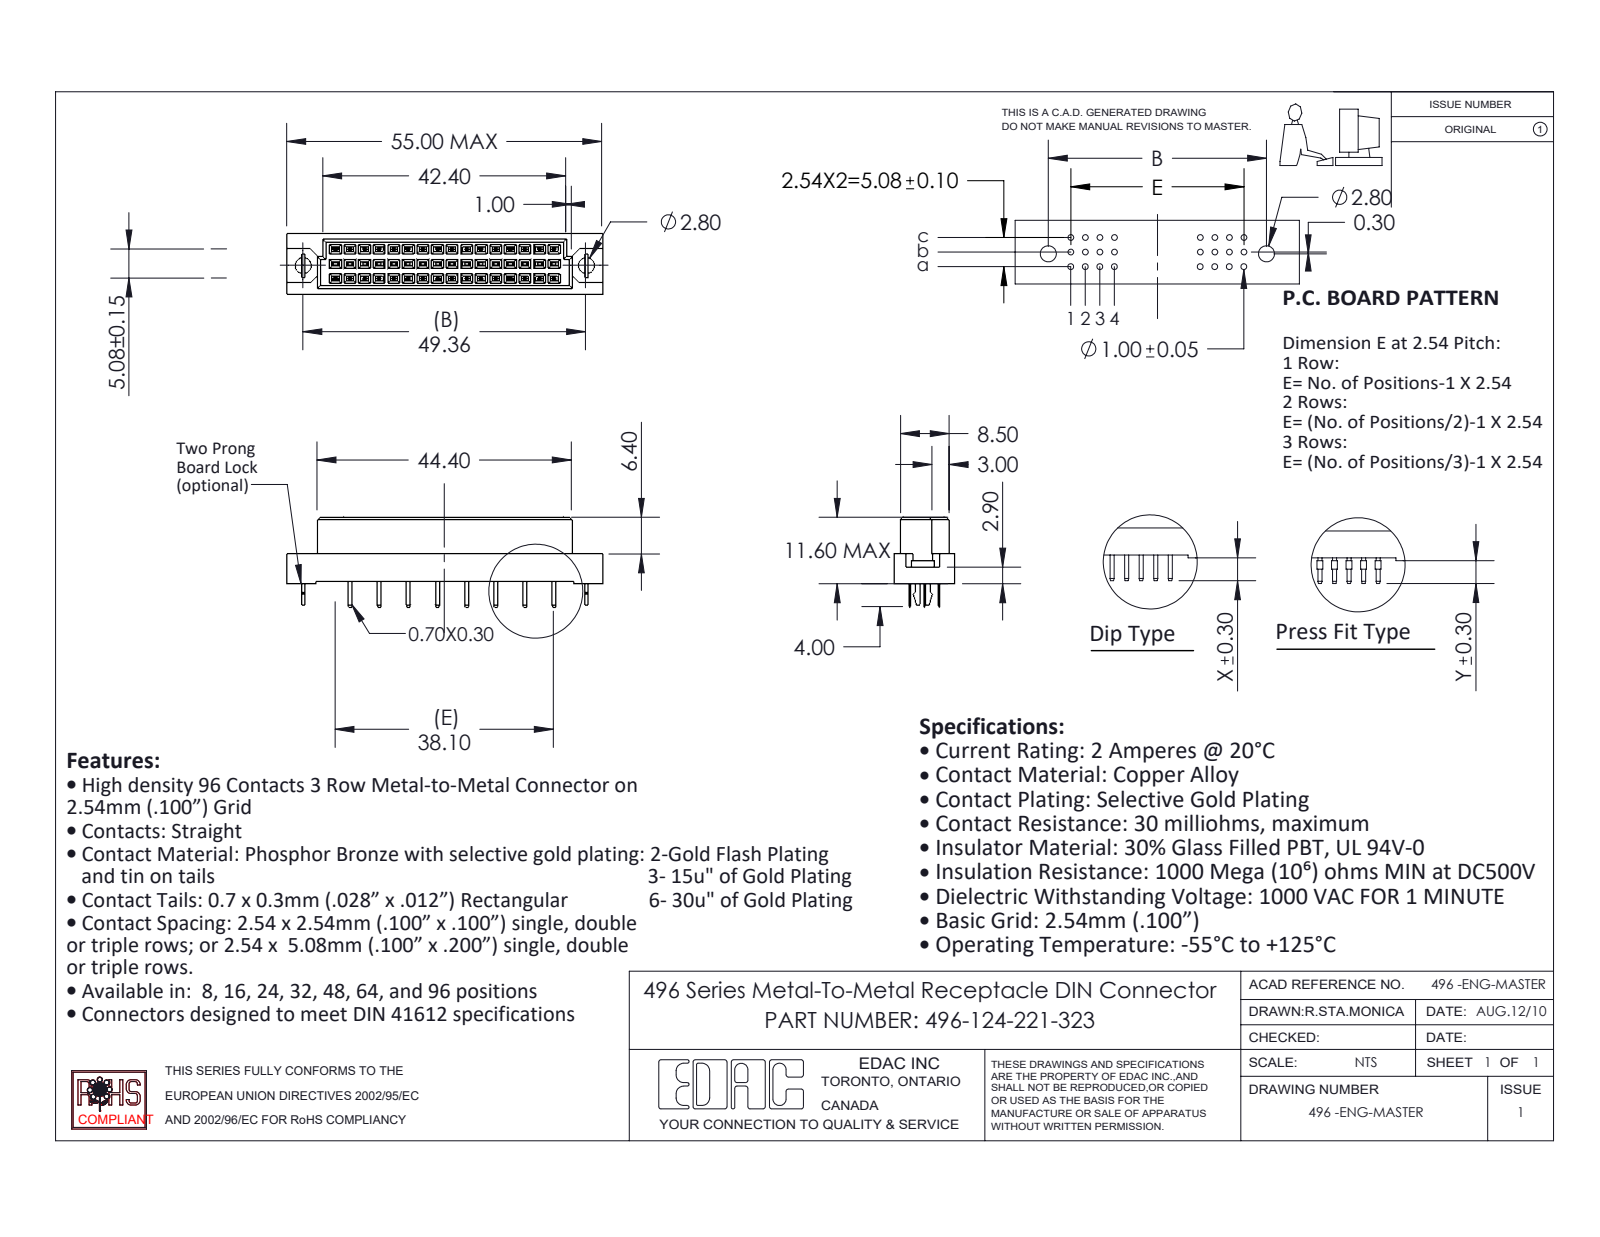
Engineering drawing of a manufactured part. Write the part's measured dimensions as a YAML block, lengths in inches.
part_name: "496 Bore-lock; 496-124-221-323; 496 Part_48; 496-290_21"
step_written_by: "SolidWorks 2020 (CONFIG_CONTROL_DESIGN)"
units: inches
bodies: {solids: 27, faces: 942, planar: 936, cylindrical: 6, other: 0}
overall_size: [2.165, 0.614, 0.417]
volume: 0.284
surface_area: 7.335
round_holes:
  - {diameter: 0.11, count: 2}
partial_cylinders:
  - {radius: 0.021, count: 1}
face_to_face_distances: [0.1, 0.2, 0.041, 0.376, 0.032, 0.022, 0.022, 0.417, 0.132, 0.068]
hole_center_spacings: [1.943]
